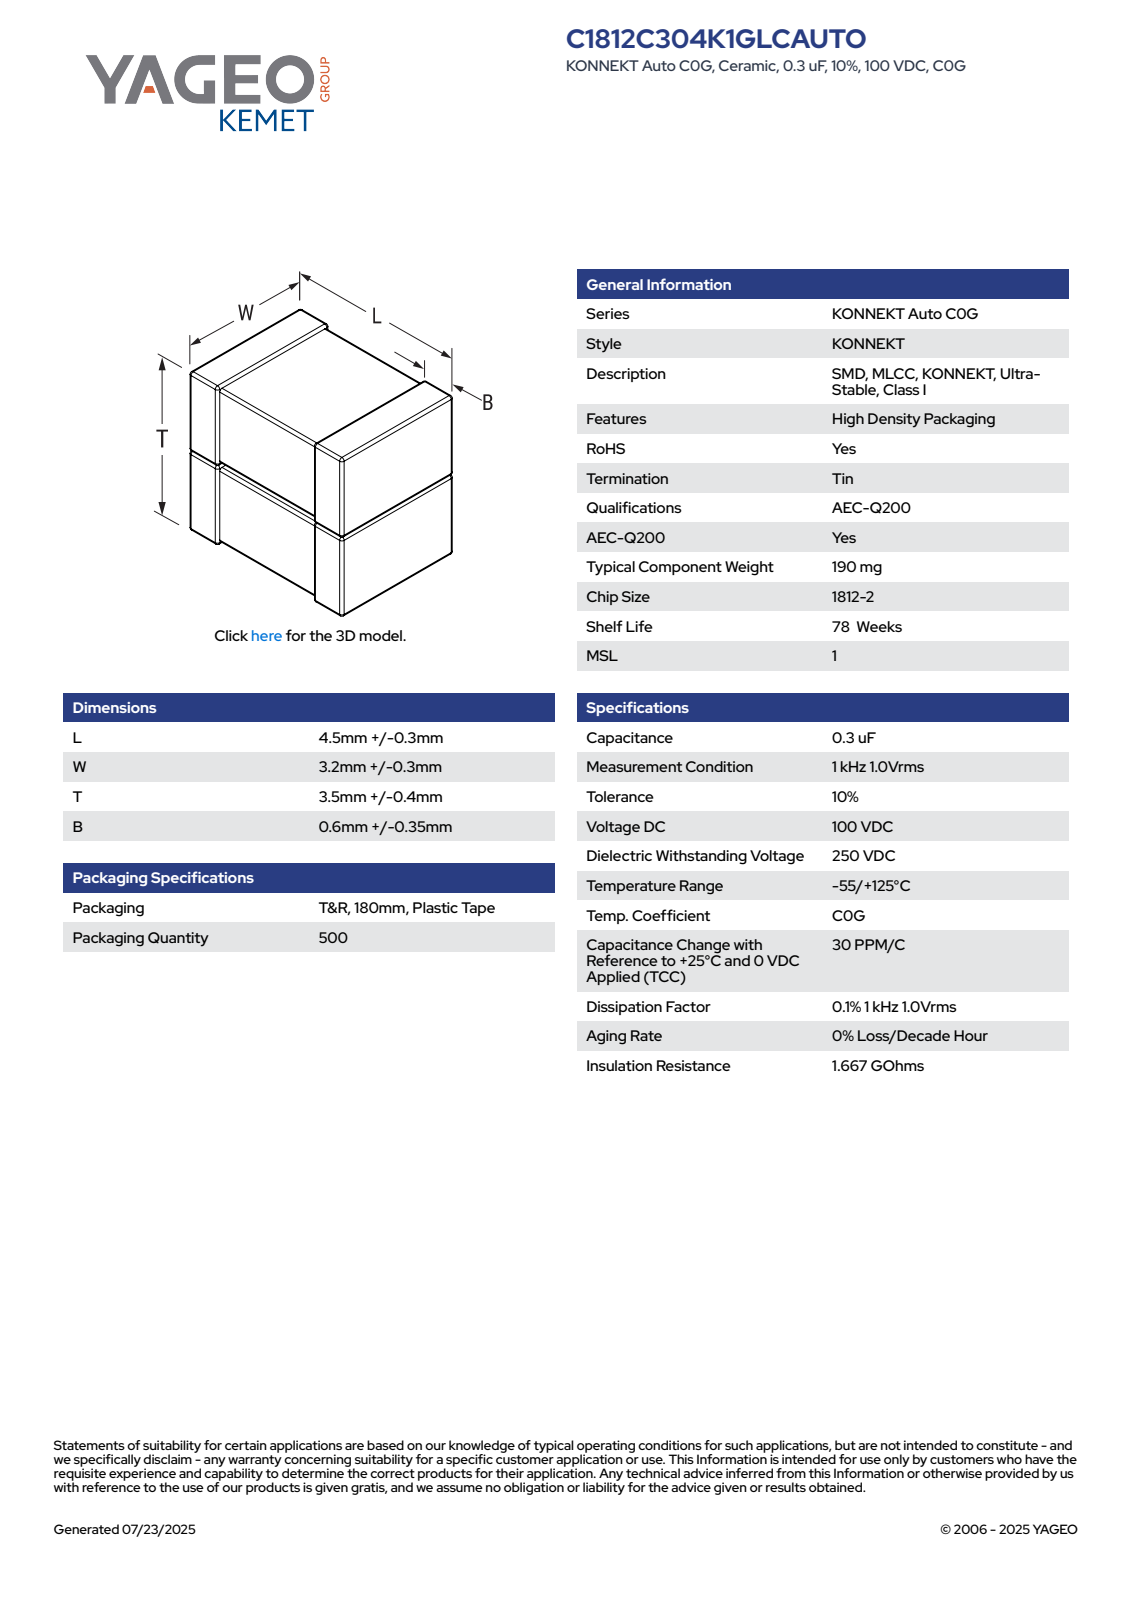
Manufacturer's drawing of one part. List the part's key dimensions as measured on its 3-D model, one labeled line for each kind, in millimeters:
Part name (STEP PRODUCT): CCSS_K2T_1812-2_L4.8W3.5B0.95T3.9
STEP written by: SolidWorks 2020 (AUTOMOTIVE_DESIGN)
Units: millimetres
Bodies: 4 solids, 189 faces (81 planar, 76 cylindrical, 32 other)
Overall size (bounding box): 4.8 × 3.9 × 3.5
Volume: 61 mm³ · Surface area: 118 mm²
Main face-to-face distances: 1.81, 1.95, 4.8, 3.43, 1.88, 2.02, 3.83, 3.36, 3.76, 3.5
